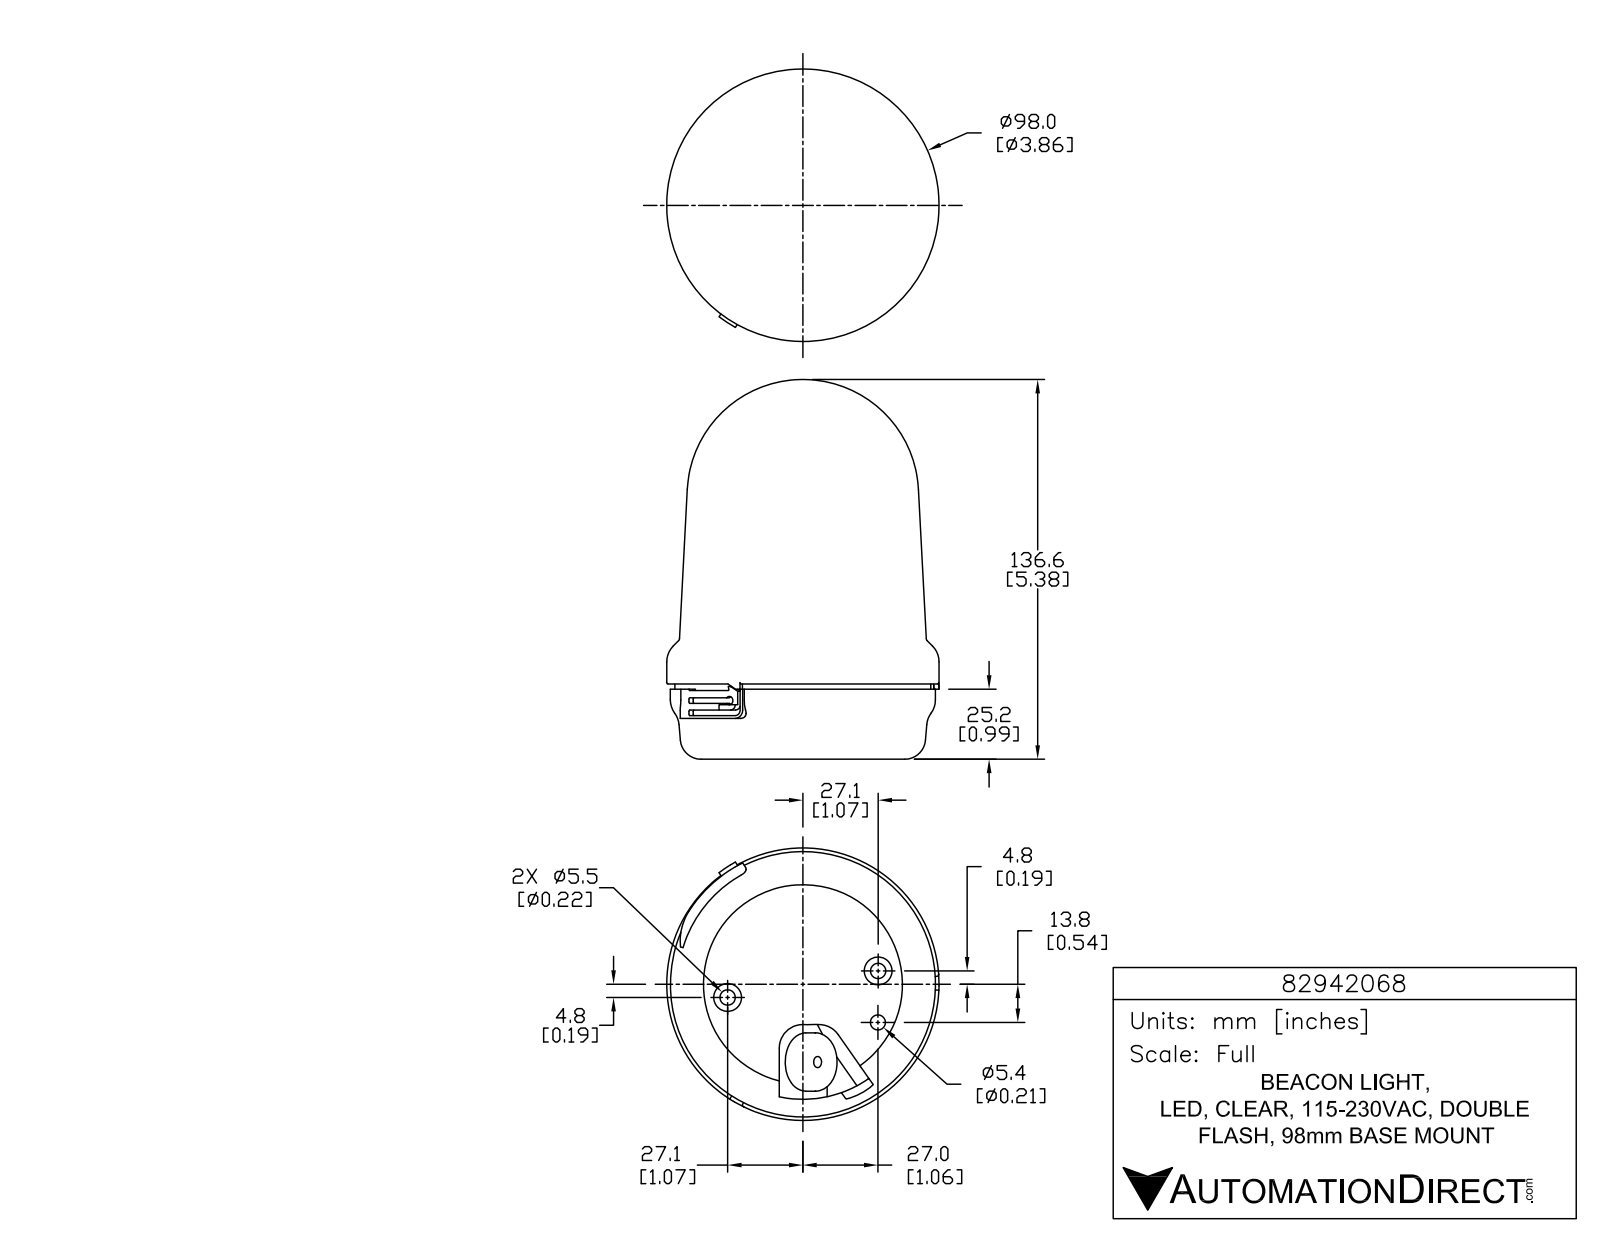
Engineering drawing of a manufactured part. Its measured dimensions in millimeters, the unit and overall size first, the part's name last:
Units: millimetres
Overall size (bounding box): 136.6 × 98 × 98
Round holes (diameter × count): ⌀1.5 ×3, ⌀5.5 ×2, ⌀4 ×1, ⌀5.4 ×1, ⌀71.6 ×1
Round bosses / shafts (diameter × count): ⌀8.6 ×3, ⌀2.1 ×3, ⌀10 ×2, ⌀98 ×1, ⌀95.4 ×1, ⌀92.1 ×1, ⌀21 ×1
Partial cylindrical surfaces — rounded edges, fillets, slot ends (radius × count): R0.1 ×9, R0.1 ×6, R0.3 ×6, R0.3 ×6, R0.3 ×6, R5 ×6, R0.5 ×5, R1 ×4
Main face-to-face distances: 26.5, 24.7, 1.9, 0.5, 25.2, 27.1, 6, 14.7, 14.2, 10.5
Hole centre spacings: 27.5, 18.5, 30.3, 54.8, 55
Volume: 732 300 mm³ · Surface area: 47 520 mm²
Bodies: 1 solid, 872 faces (566 planar, 204 cylindrical, 102 other)
Part name (STEP PRODUCT): 82942068
STEP written by: SolidWorks 2015 (AUTOMOTIVE_DESIGN)
